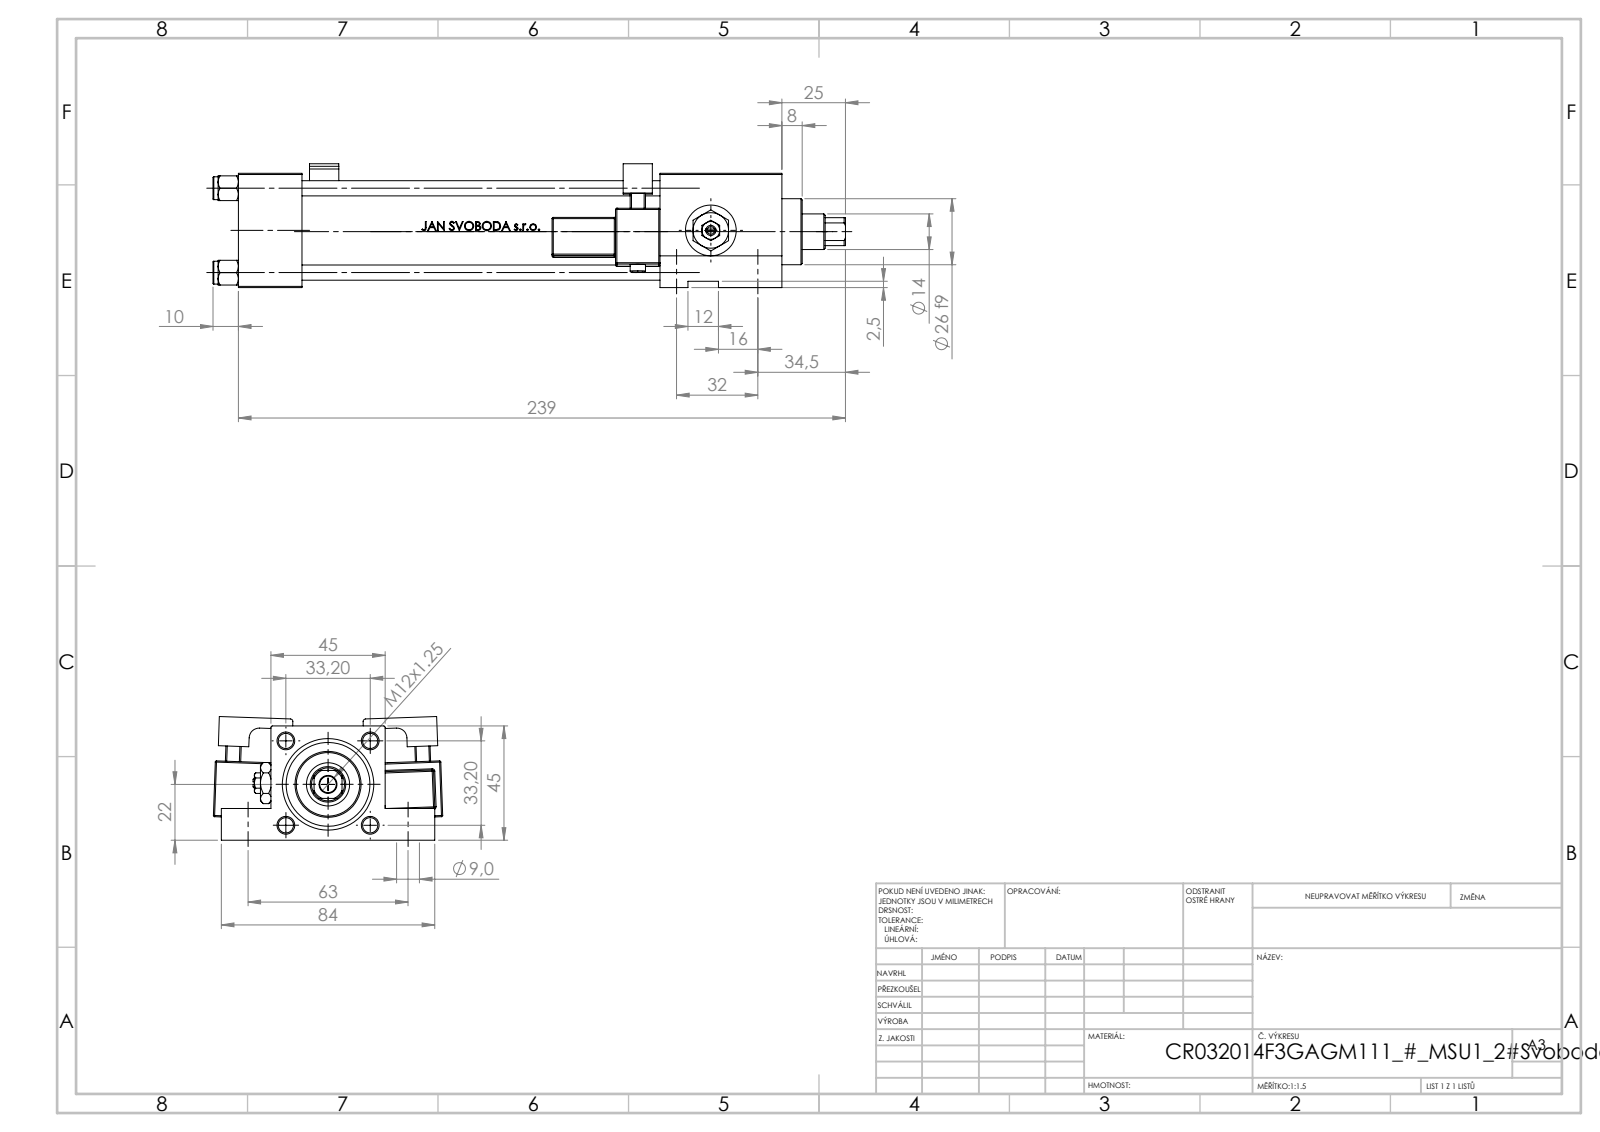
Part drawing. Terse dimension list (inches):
name: NUT_M5_F; V215CR_F_Body; V215CR_MSU; Zatka_pro_OIL_PORT (+3 more)
written by: SolidWorks 2019 (CONFIG_CONTROL_DESIGN)
unit: in
bodies: 15 solids, 1353 faces (543 planar, 192 cylindrical, 618 other)
size: 9.803 × 3.556 × 1.918
volume: 18.73 in³; area: 181.7 in²
holes: 4× ⌀0.236, 4× ⌀0.354, 3× ⌀0.276, 3× ⌀0.787, 2× ⌀0.518, 1× ⌀0.256, 1× ⌀0.512, 1× ⌀0.551, 1× ⌀0.669, 1× ⌀0.945, 1× ⌀1.26, 1× ⌀1.299
bosses: 4× ⌀0.354, 2× ⌀0.236, 1× ⌀1.496, 1× ⌀1.024
rounds: 48× R0.02, 2× R0.039, 2× R0.098, 2× R0.157, 1× R0.256
face distances: 1.772, 0.984, 0.118, 5.551, 7.441, 6.535, 0.492, 1.673, 8.425, 1.89
hole spacings: 1.307, 0.911, 0.938, 1.26, 1.848, 2.48, 2.782, 6.42
